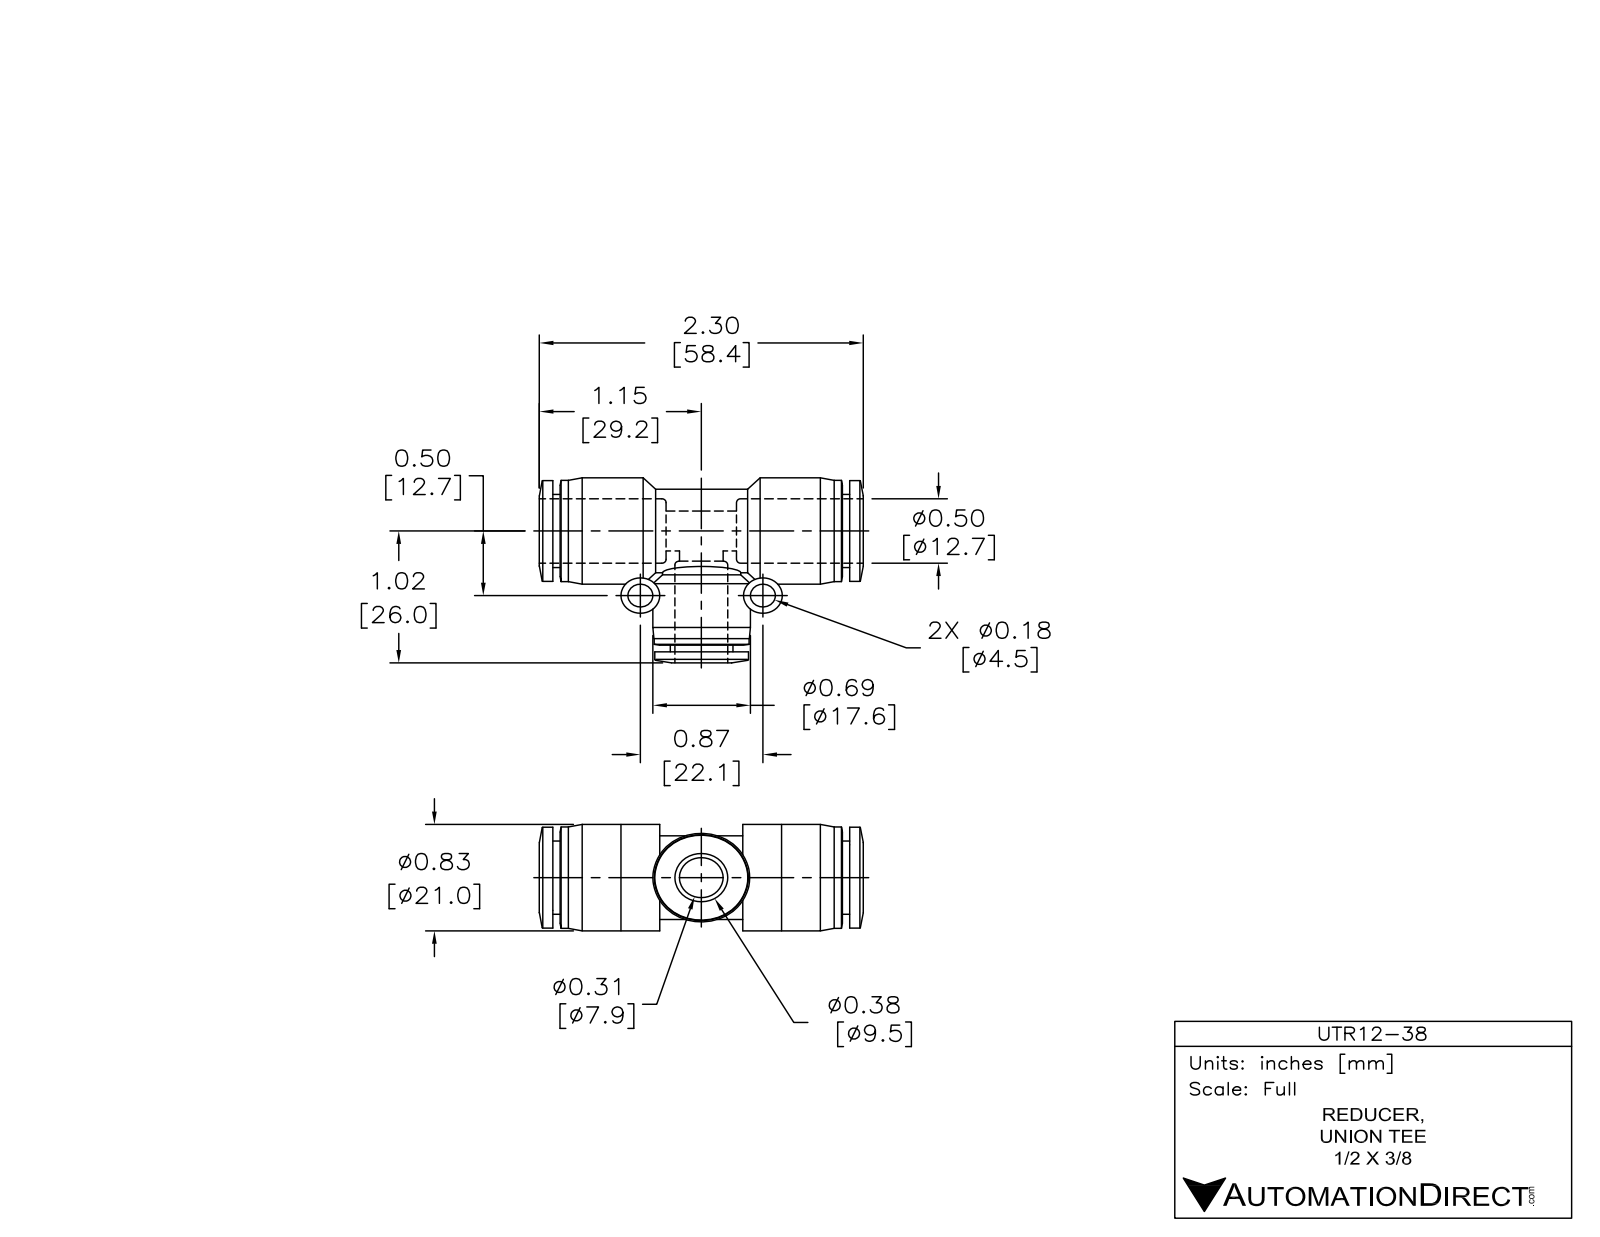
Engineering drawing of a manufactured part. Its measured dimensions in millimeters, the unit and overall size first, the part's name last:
Units: millimetres
Overall size (bounding box): 58.5 × 36.8 × 21
Round holes (diameter × count): ⌀4.5 ×2, ⌀8 ×2, ⌀9.8 ×1, ⌀13 ×1
Round bosses / shafts (diameter × count): ⌀7 ×2, ⌀21 ×1, ⌀20 ×1, ⌀19.9 ×1, ⌀17.5 ×1, ⌀17 ×1, ⌀16.8 ×1, ⌀16.5 ×1
Main face-to-face distances: 1.3, 52.3, 20.7, 32.9, 19.4, 31.6, 53.6, 51, 12.3, 21
Hole centre spacings: 22
Volume: 13 400 mm³ · Surface area: 10 030 mm²
Bodies: 1 solid, 103 faces (14 planar, 47 cylindrical, 42 other)
Part name (STEP PRODUCT): UTR12-38
STEP written by: SolidWorks 2015 (AUTOMOTIVE_DESIGN)
